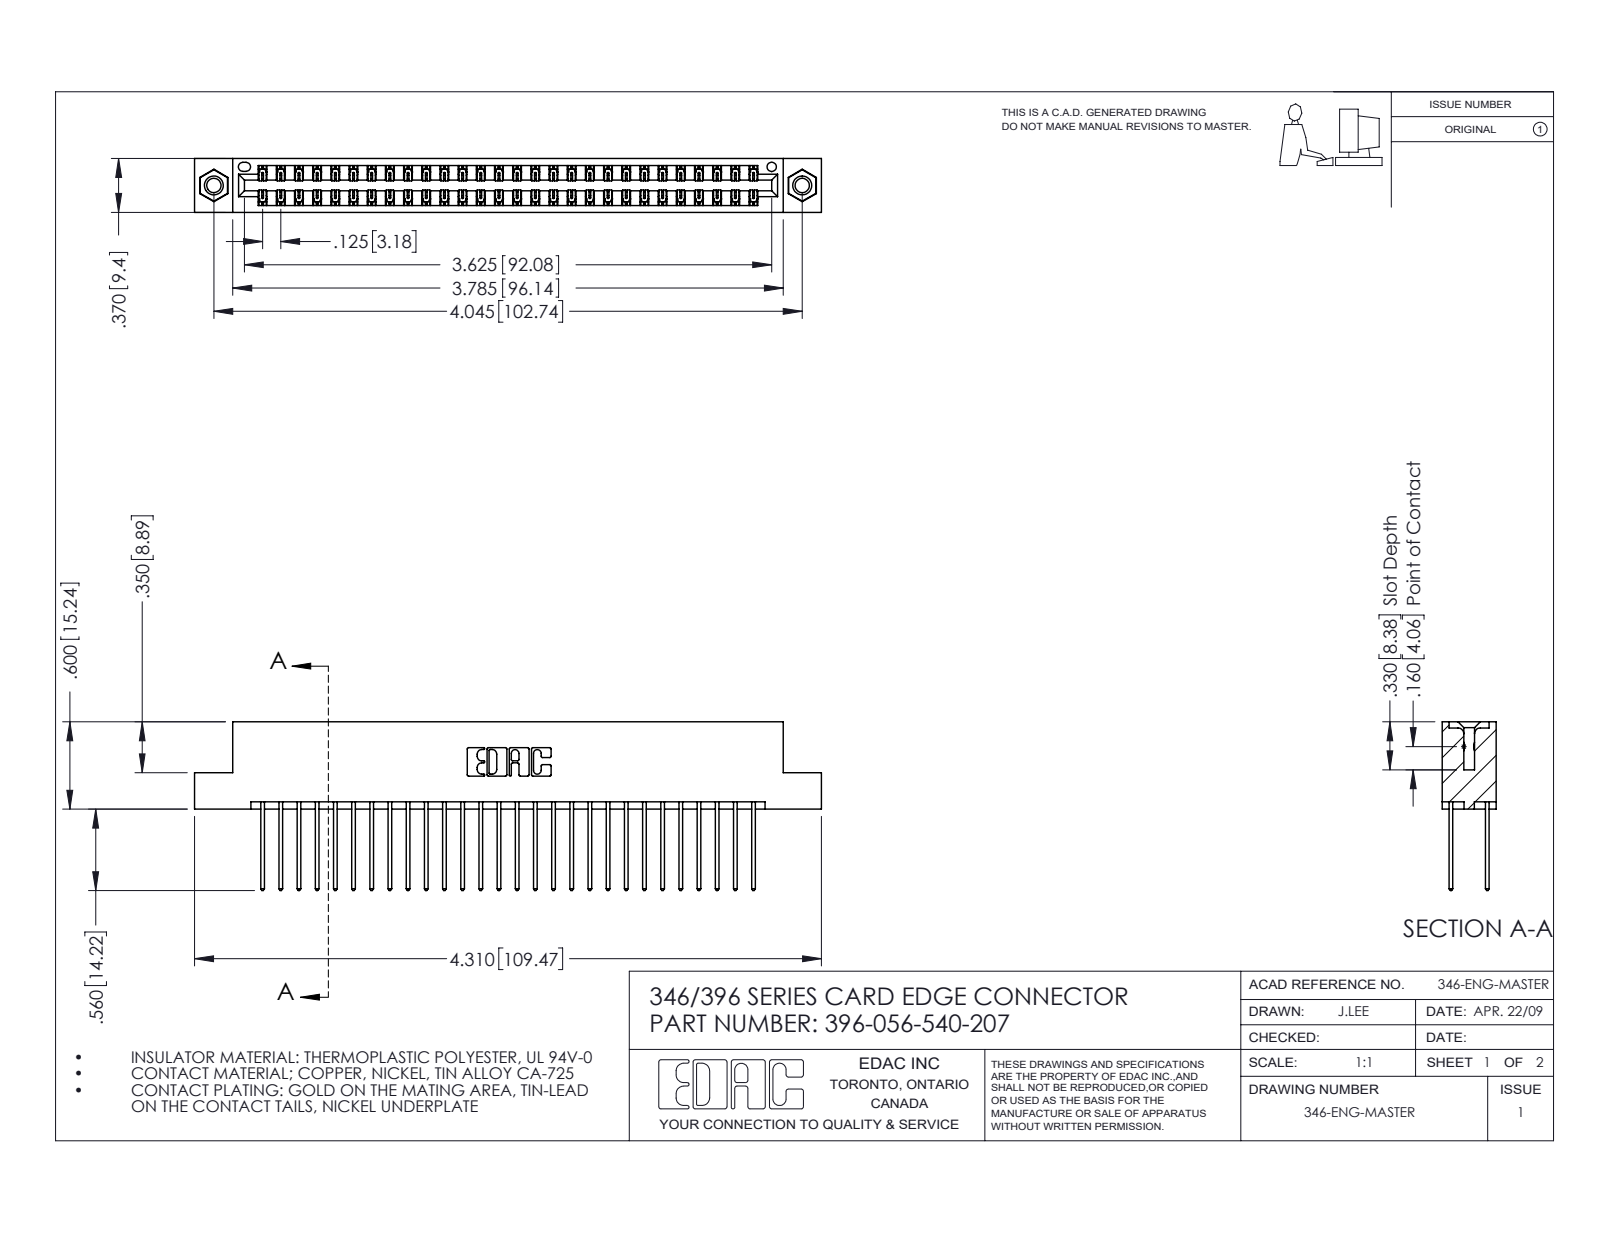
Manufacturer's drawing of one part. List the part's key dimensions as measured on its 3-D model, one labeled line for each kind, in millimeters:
Part name (STEP PRODUCT): 345-250-001_345-250-005-103; 345-292-001_345-293-140; 396-056-540-207; 346 Part_Flush Mounting Lugs - 0.156 Dia-TI
STEP written by: SolidWorks 2016 (CONFIG_CONTROL_DESIGN)
Units: millimetres
Bodies: 59 solids, 3094 faces (2068 planar, 1010 cylindrical, 16 other)
Overall size (bounding box): 109.5 × 29.5 × 9.4
Volume: 10 800 mm³ · Surface area: 15 610 mm²
Round holes (diameter × count): ⌀2.5 ×2, ⌀3.2 ×2, ⌀4 ×2, ⌀1.6 ×1
Round bosses / shafts (diameter × count): ⌀3.9 ×2
Partial cylindrical surfaces — rounded edges, fillets, slot ends (radius × count): R0.2 ×84, R0.3 ×56, R0.3 ×22, R0.2 ×6, R0.8 ×6, R0.7 ×3, R0.4 ×2, R0.6 ×2
Main face-to-face distances: 1.2, 8.2, 6.4, 1.8, 7.6, 0.6, 9.4, 7, 3.8, 5.6
Hole centre spacings: 6.2, 97.5, 102.7
